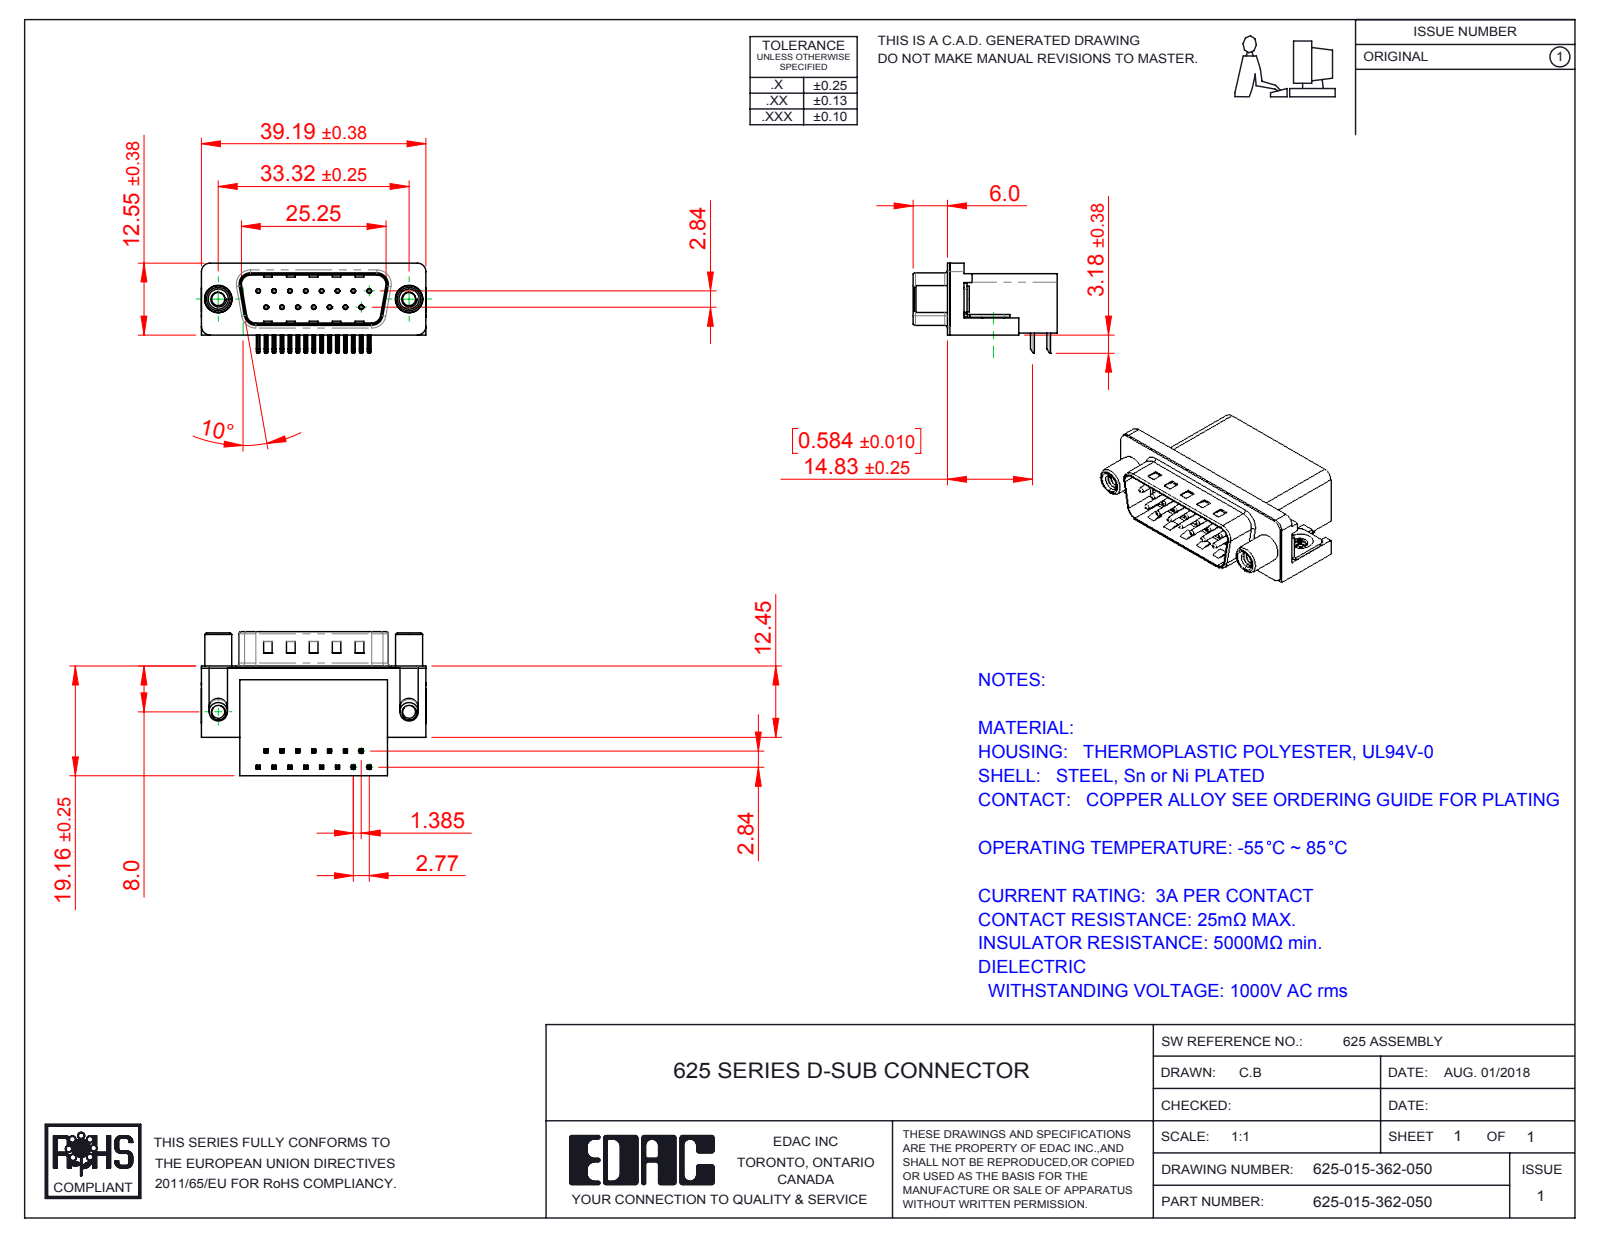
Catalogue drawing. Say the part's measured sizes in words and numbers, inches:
The part is named "625 Shell_15 Socket; 625 Housing_15 Socket; 625 4-40 Threaded Board Mount; 625 Round Threaded Standoff (+3 more)". Its 3-D file was written by "SolidWorks 2016 (CONFIG_CONTROL_DESIGN)". It is 21 solids with 1505 faces: 887 planar, 467 cylindrical and 151 other. Overall it measures 1.544 by 0.991 by 0.619 inches. Its volume is 0.387 cubic inches and its surface area 10.39 square inches. Round holes: 15 of diameter 0.014, 15 of diameter 0.031, 2 of diameter 0.089, 2 of diameter 0.091, 2 of diameter 0.122, 2 of diameter 0.157, 2 of diameter 0.189, 2 of diameter 0.197. Round bosses or shafts: 15 of diameter 0.03, 2 of diameter 0.193, 2 of diameter 0.185, 2 of diameter 0.177, 2 of diameter 0.152, 2 of diameter 0.128. Partial cylindrical surfaces (rounded edges, fillets, slot ends): 60 of radius 0.01, 30 of radius 0.005, 16 of radius 0.039, 9 of radius 0.02, 8 of radius 0.063, 6 of radius 0.059, 4 of radius 0.035, 4 of radius 0.079. The main face-to-face distances are 0.016, 0.407, 0.739, 0.083, 0.412, 0.067, 0.428, 0.754, 0.345, 0.64. The hole center spacings are 0.124, 0.109, 0.218, 0.327, 0.436, 0.198, 0.198, 0.294.
